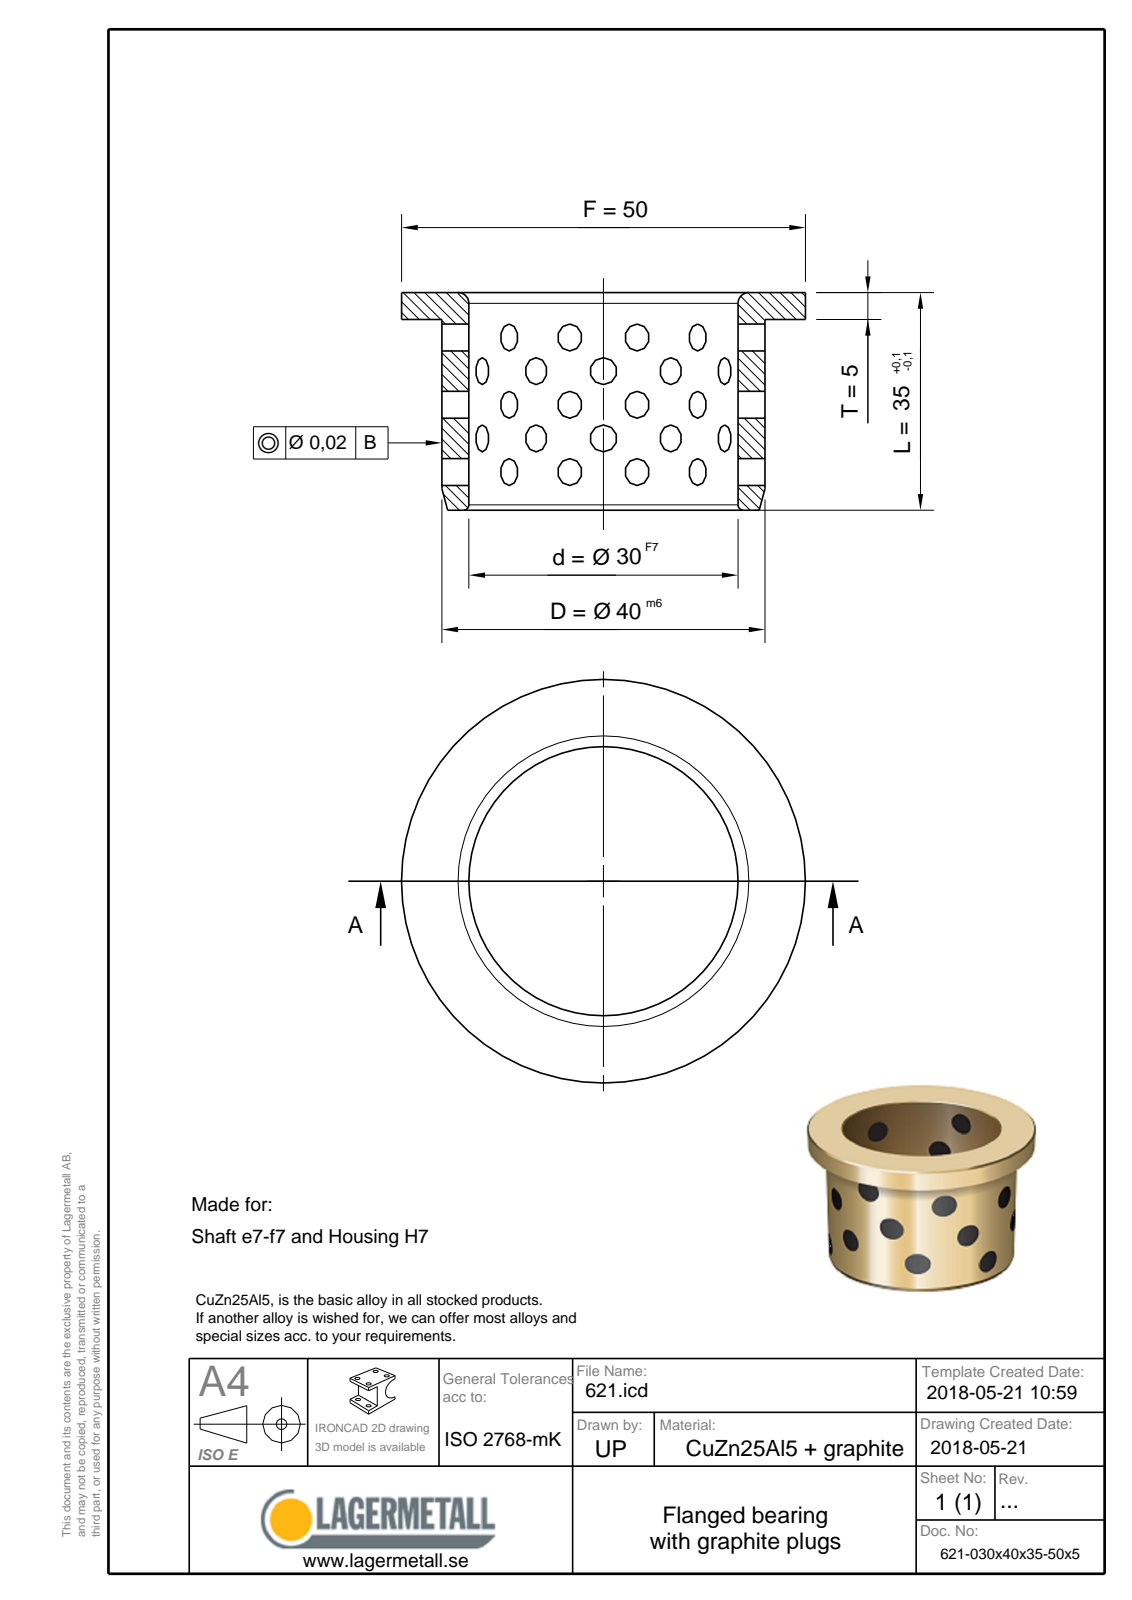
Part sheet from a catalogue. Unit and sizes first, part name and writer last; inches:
Units: inches
Overall size (bounding box): 1.969 × 1.969 × 1.378
Round holes (diameter × count): ⌀1.181 ×1
Round bosses / shafts (diameter × count): ⌀1.969 ×1, ⌀1.575 ×1
Main face-to-face distances: 0.197, 1.181, 1.378
Volume: 1.377 in³ · Surface area: 15.72 in²
Bodies: 1 solid, 9 faces (3 planar, 3 cylindrical, 3 other)
Part name (STEP PRODUCT): 621-030x40x35-50x5
STEP written by: Spatial InterOp 3D (CONFIG_CONTROL_DESIGN)
